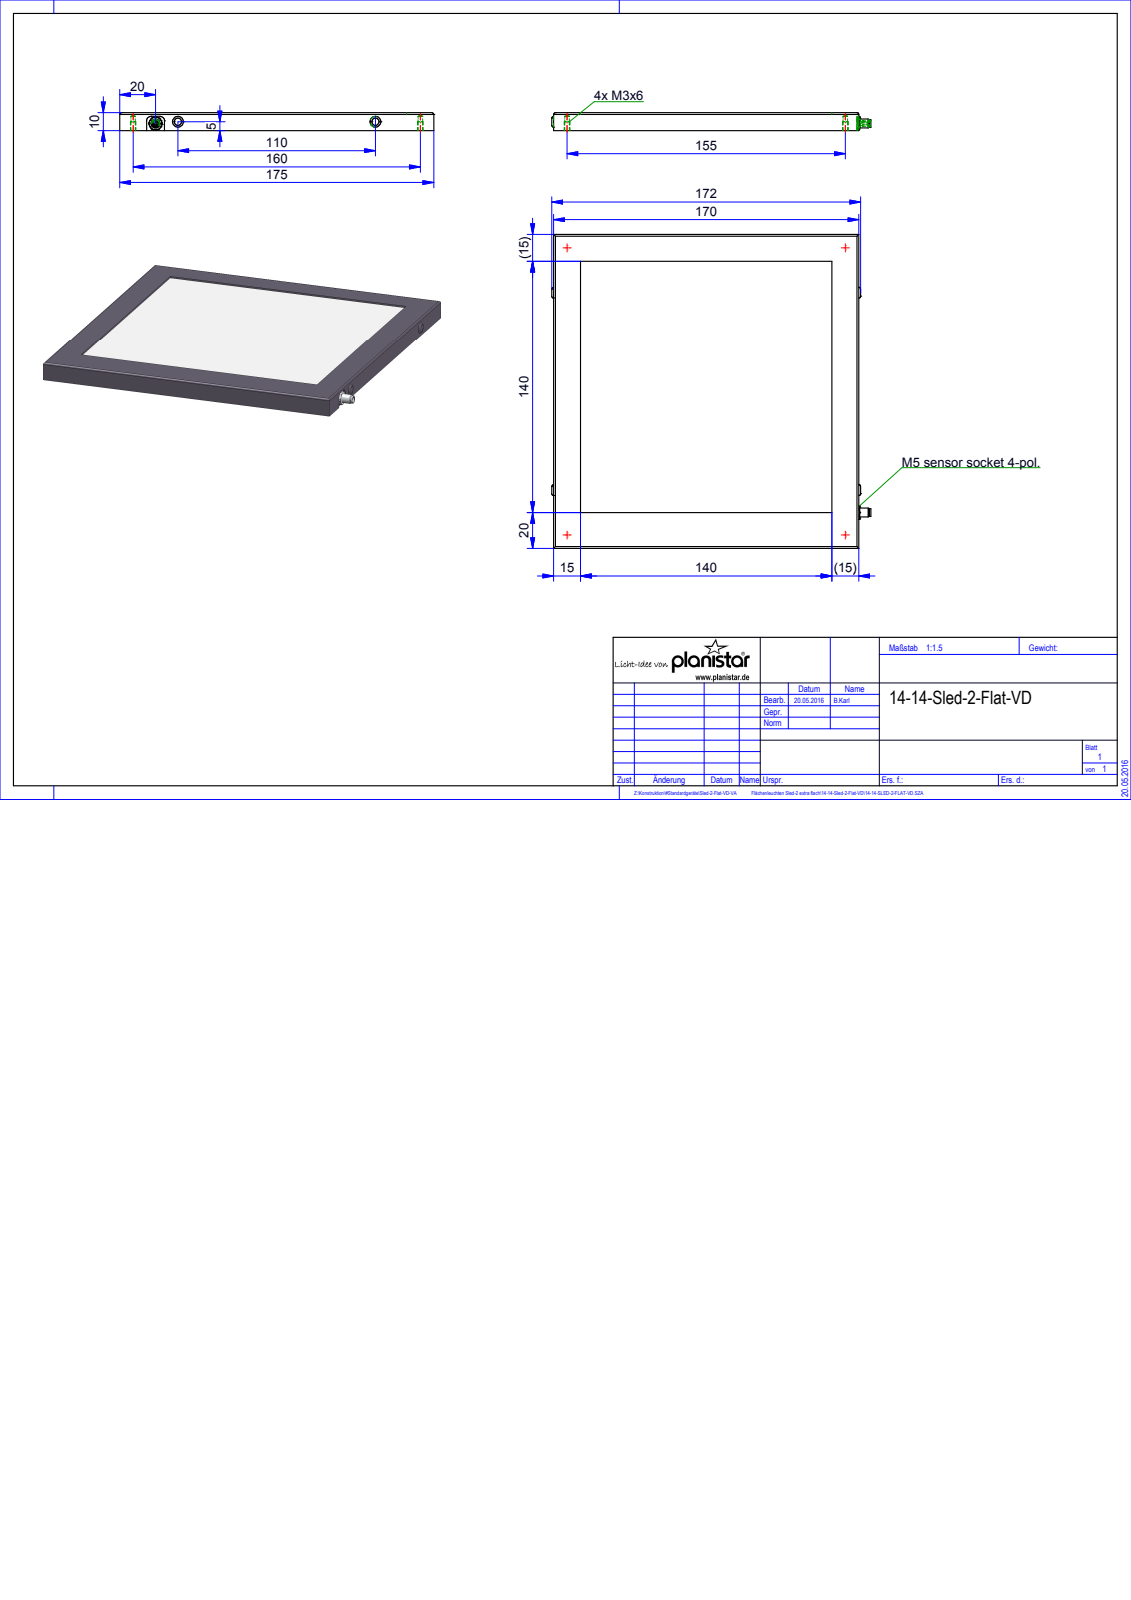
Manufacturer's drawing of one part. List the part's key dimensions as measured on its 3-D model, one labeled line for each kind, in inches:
Part name (STEP PRODUCT): Root; Baugruppe_Xled-2-VD; Teil; QUADER_0
STEP written by: HiCAD 2015 2002.1 Build 408 (AUTOMOTIVE_DESIGN)
Units: inches
Bodies: 4 solids, 99 faces (41 planar, 31 cylindrical, 27 other)
Overall size (bounding box): 6.996 × 6.89 × 0.394
Volume: 16.95 in³ · Surface area: 104.4 in²
Round holes (diameter × count): ⌀0.098 ×4, ⌀0.118 ×4, ⌀0.035 ×1, ⌀0.126 ×1, ⌀0.176 ×1
Round bosses / shafts (diameter × count): ⌀0.019 ×4, ⌀0.197 ×1, ⌀0.169 ×1, ⌀0.167 ×1
Partial cylindrical surfaces — rounded edges, fillets, slot ends (radius × count): R0.039 ×4, R0.098 ×2, R0.008 ×1, R0.148 ×1
Main face-to-face distances: 0.354, 0.039, 0.394, 6.89, 6.693, 0.591, 6.102, 5.512, 6.299, 0.787
Hole centre spacings: 6.102, 6.299, 8.77, 0.035
